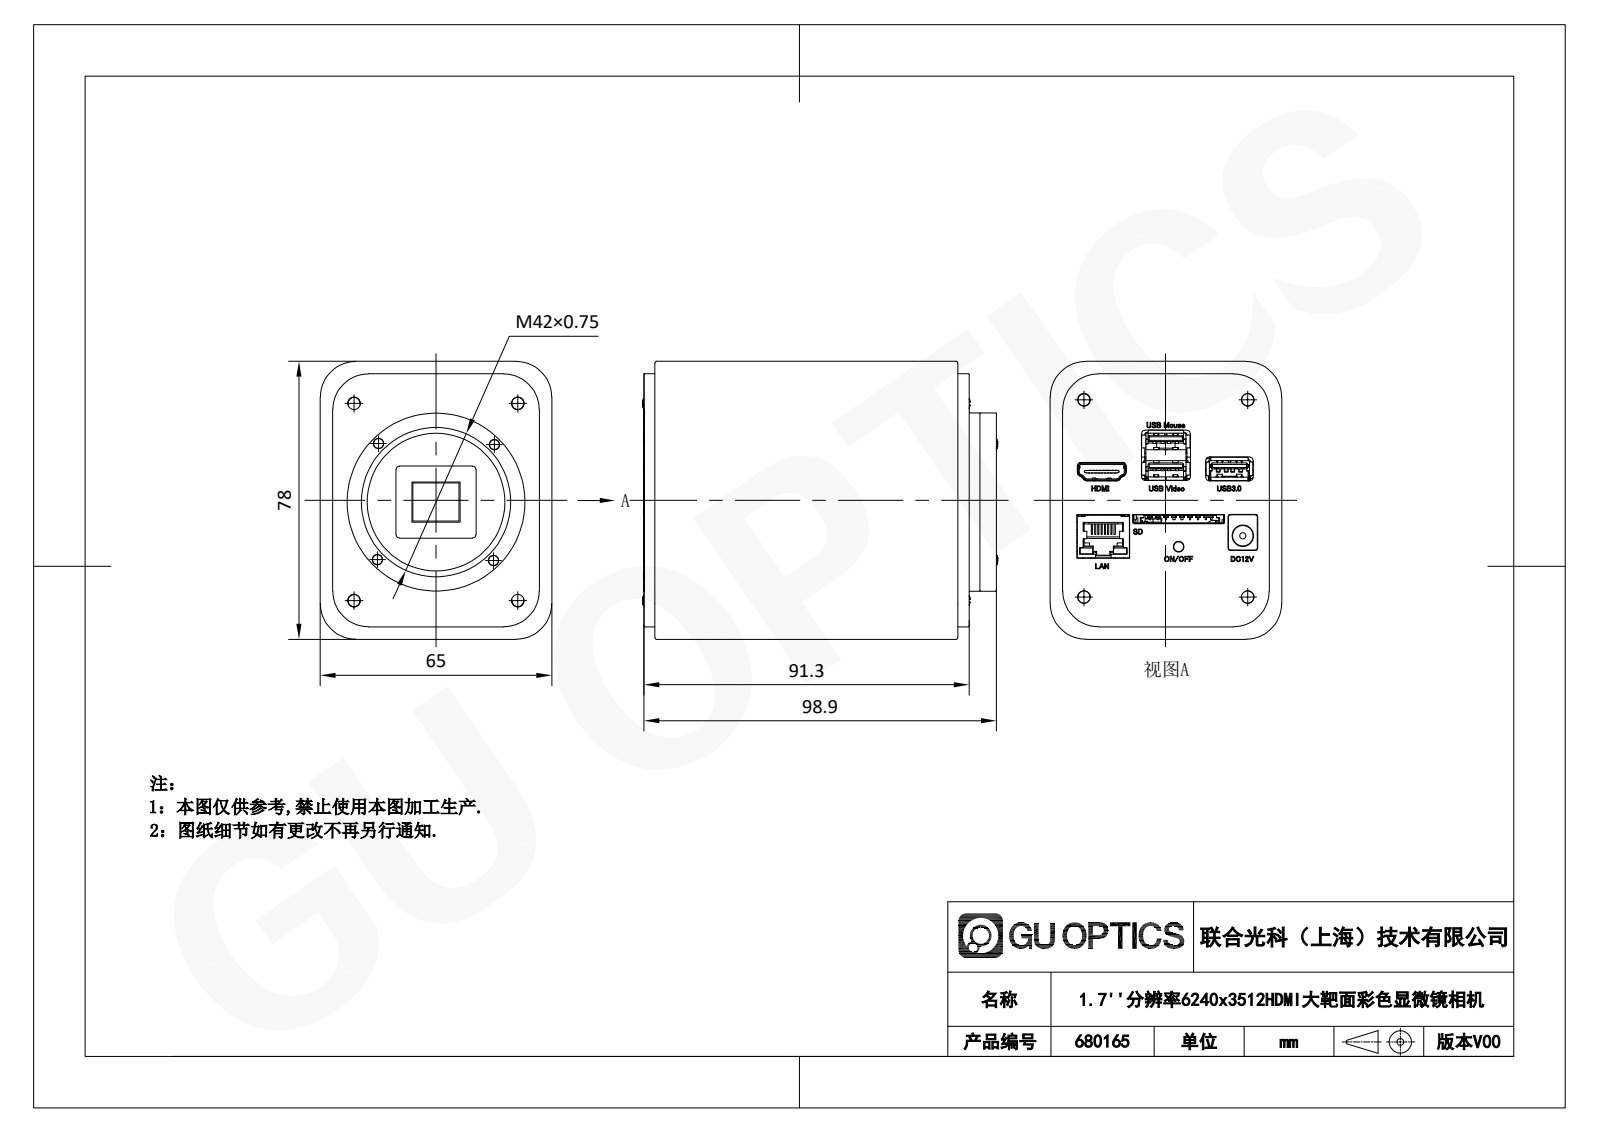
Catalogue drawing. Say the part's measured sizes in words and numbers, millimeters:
The part is named "680165". Its 3-D file was written by "SolidWorks 2020 (CONFIG_CONTROL_DESIGN)". It is 0 solids with 11738 faces: 7686 planar, 2027 cylindrical and 2025 other. Overall it measures 99.61 by 78 by 65 millimeters. Round holes: 13 of diameter 1.98, 5 of diameter 1.44, 5 of diameter 2.25, 4 of diameter 0.72, 4 of diameter 3, 4 of diameter 3.52, 1 of diameter 1.62, 1 of diameter 2.88, 1 of diameter 3.05, 1 of diameter 3.34, 1 of diameter 5.76, 1 of diameter 38.67. Round bosses or shafts: 12 of diameter 1.8, 6 of diameter 3.5, 6 of diameter 2, 5 of diameter 3.15, 5 of diameter 2.83, 5 of diameter 1.62, 4 of diameter 3.6, 4 of diameter 2.8. Partial cylindrical surfaces (rounded edges, fillets, slot ends): 127 of radius 0.18, 126 of radius 0.1, 85 of radius 0.27, 82 of radius 0.45, 50 of radius 0.14, 36 of radius 0.2, 23 of radius 0.23, 23 of radius 0.9. The main face-to-face distances are 0.5, 1.44, 3, 64.5, 7.74, 85, 65, 64, 82, 91.2. The hole center spacings are 26.64, 30.6, 44.63, 1.37, 3.87, 11.93, 14.54, 19.14.
